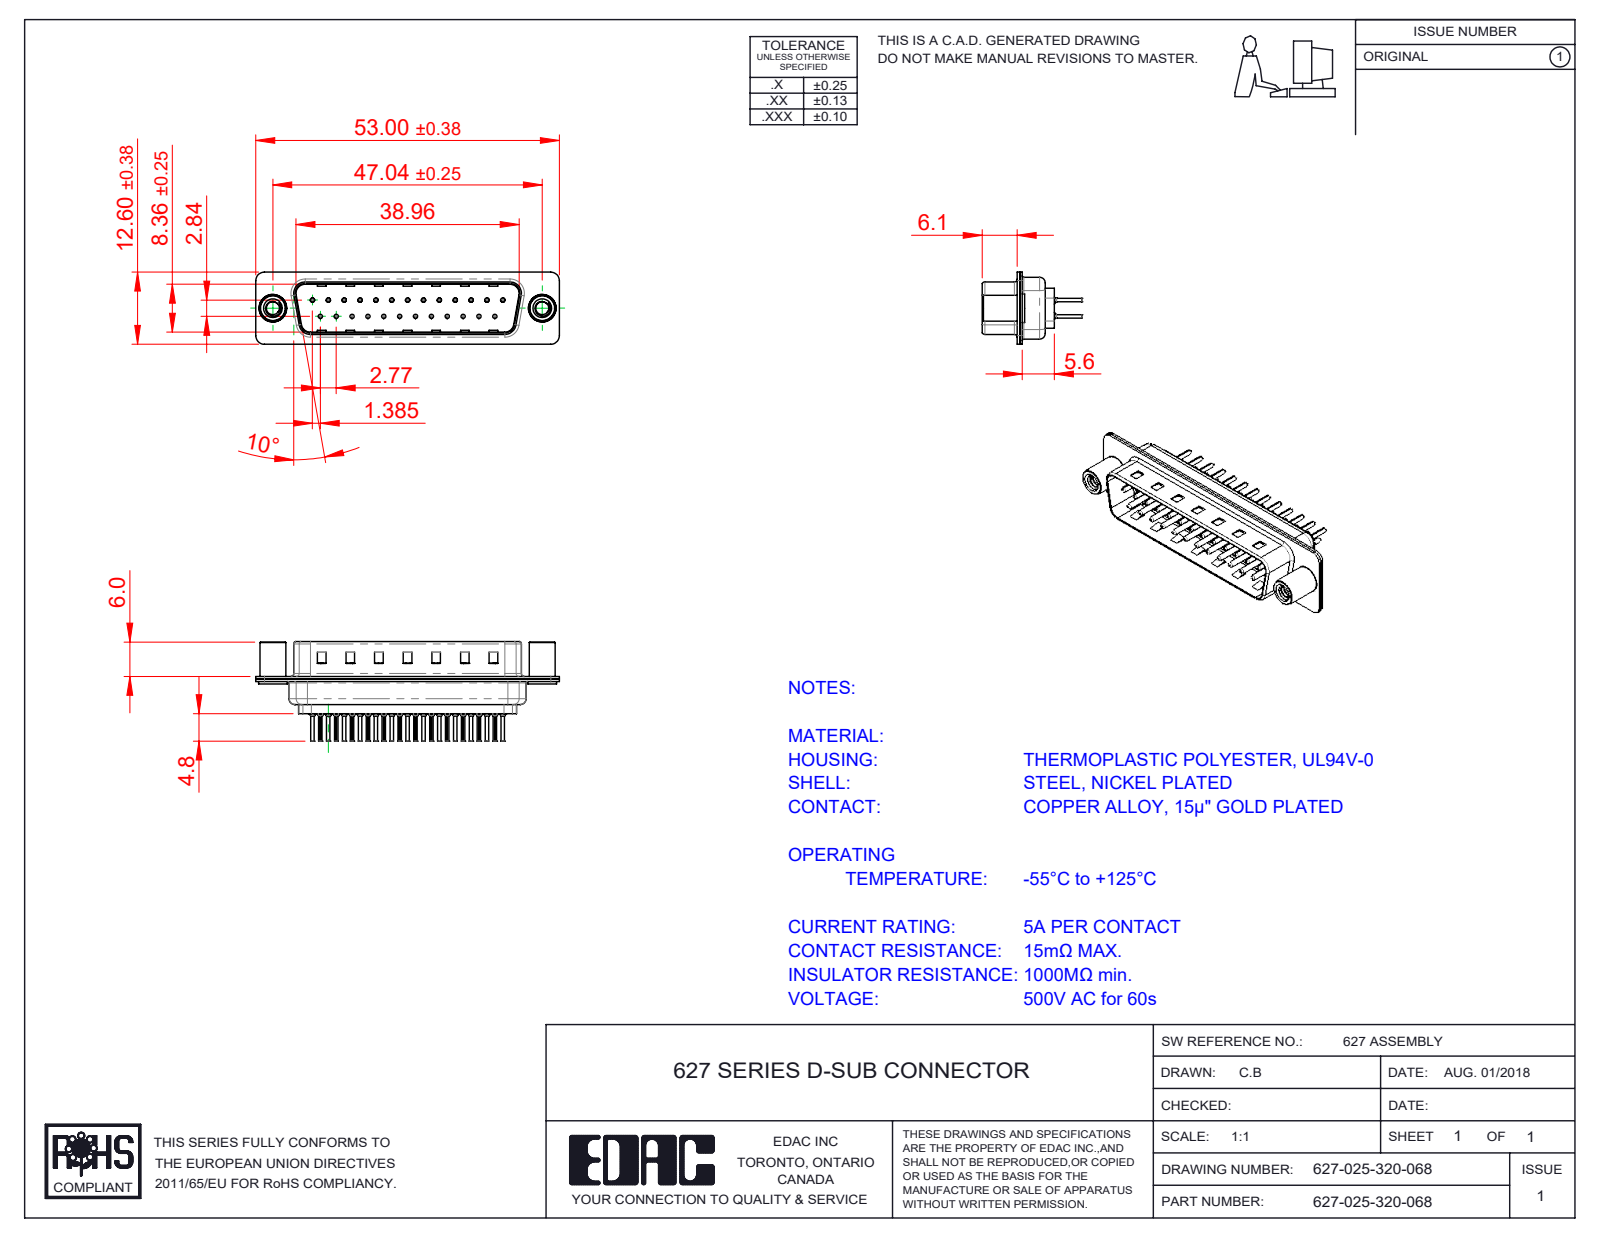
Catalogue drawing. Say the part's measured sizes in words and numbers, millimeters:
The part is named "627 4-40 Threaded Standoff; 627-025-320-068; 627 Shell Rear_25 Contacts; 627 Contact Row 1_20L (+3 more)". Its 3-D file was written by "SolidWorks 2020 (CONFIG_CONTROL_DESIGN)". It is 30 solids with 2860 faces: 773 planar, 1090 cylindrical and 997 other. Overall it measures 53 by 17.3 by 12.6 millimeters. Its volume is 2 746 cubic millimeters and its surface area 7 999 square millimeters. Round holes: 25 of diameter 0.2, 25 of diameter 0.35, 25 of diameter 1.1, 25 of diameter 1.6, 2 of diameter 2.26, 2 of diameter 4, 2 of diameter 4.8. Round bosses or shafts: 25 of diameter 2, 25 of diameter 1.5, 25 of diameter 0.75, 25 of diameter 0.6, 2 of diameter 5, 2 of diameter 4.9, 2 of diameter 4.5. Partial cylindrical surfaces (rounded edges, fillets, slot ends): 50 of radius 0.1, 16 of radius 1.5, 12 of radius 2, 8 of radius 0.5, 8 of radius 1.6, 4 of radius 0.25, 4 of radius 0.6, 4 of radius 0.65. The main face-to-face distances are 0.4, 0.45, 0.82, 9.58, 0.9, 8.76, 1.5, 1.4, 6.5, 6.05. The hole center spacings are 3.16, 8.31, 2.77, 5.54, 11.08, 16.62, 5.03, 5.04.
